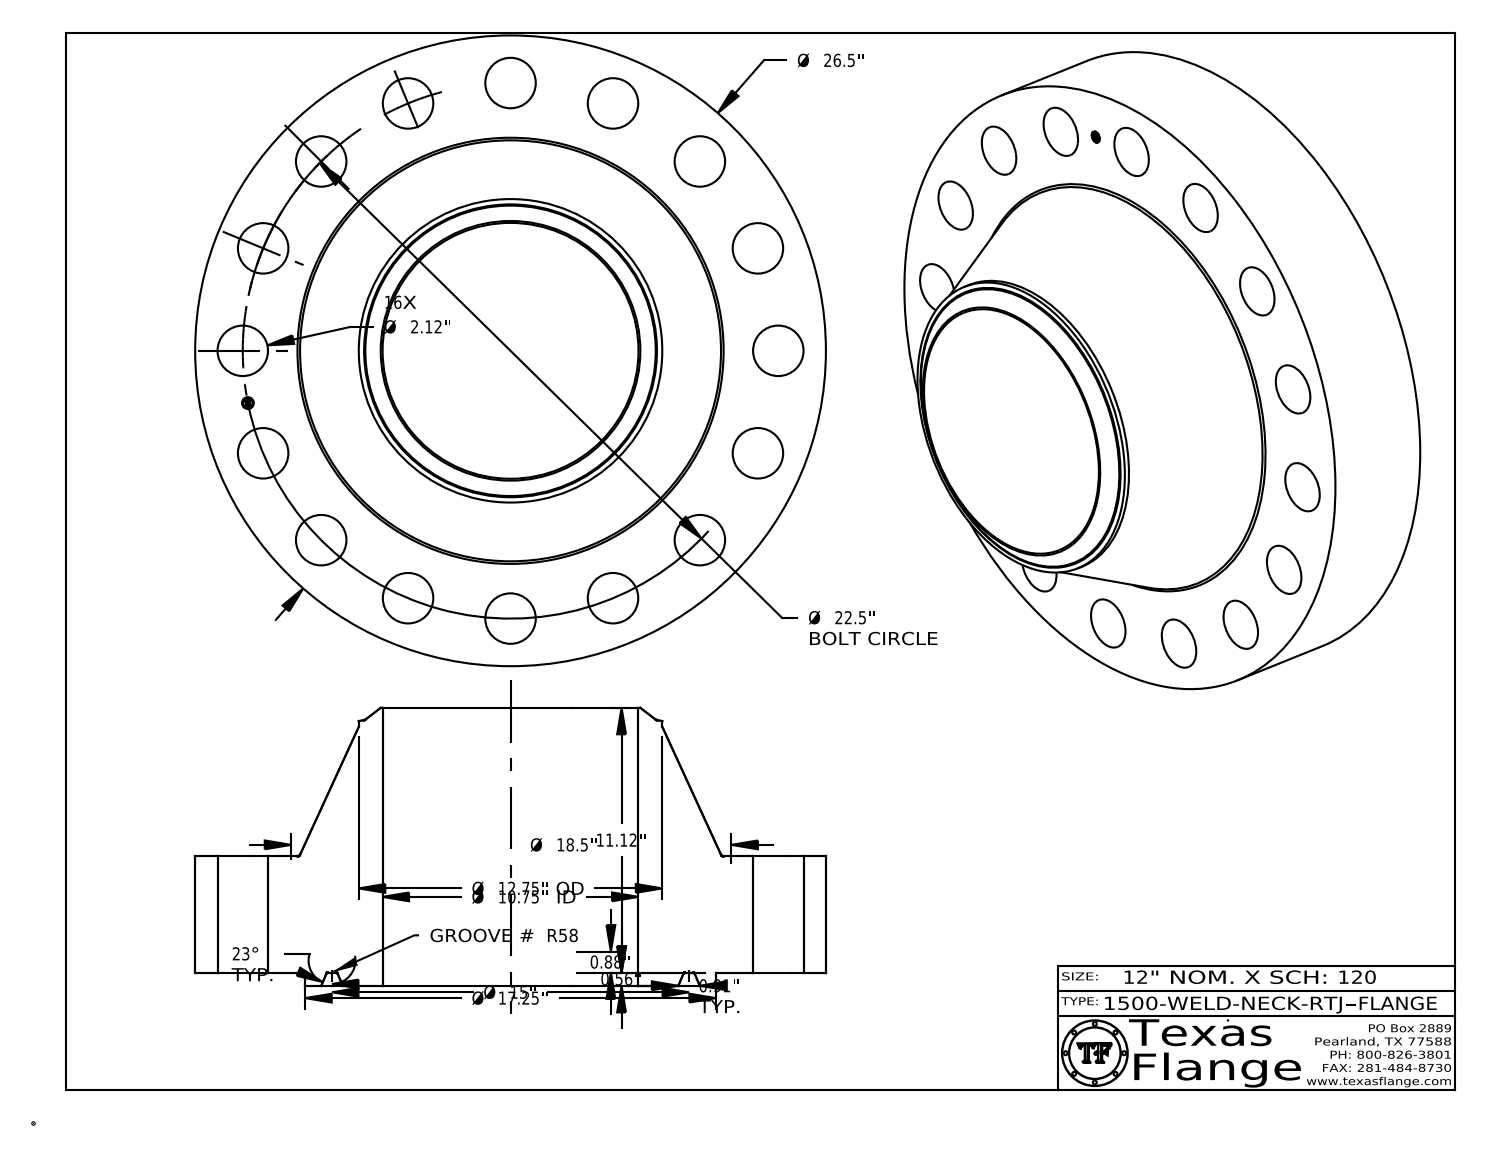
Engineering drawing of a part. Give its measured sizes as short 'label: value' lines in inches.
name: 1500-WELD-NECK-RTJ
written by: CATIA V5 STEP AP214 (AUTOMOTIVE_DESIGN)
unit: in
bodies: 1 solid, 449 faces (371 planar, 60 cylindrical, 18 other)
size: 26.5 × 26.5 × 11.683
volume: 2 563 in³; area: 2 377 in²
holes: 16× ⌀2.12, 1× ⌀0.495, 1× ⌀10.75
bosses: 8× ⌀0.03, 1× ⌀26.5, 1× ⌀17.25, 1× ⌀12.75, 1× ⌀0.39
face distances: 4.88, 0.563, 5.443, 11.683, 11.12, 6.24, 5.428, 4.865, 0.015, 6.255
hole spacings: 12.5, 20.787, 22.068, 11.25, 8.611, 15.91, 4.389, 4.39
